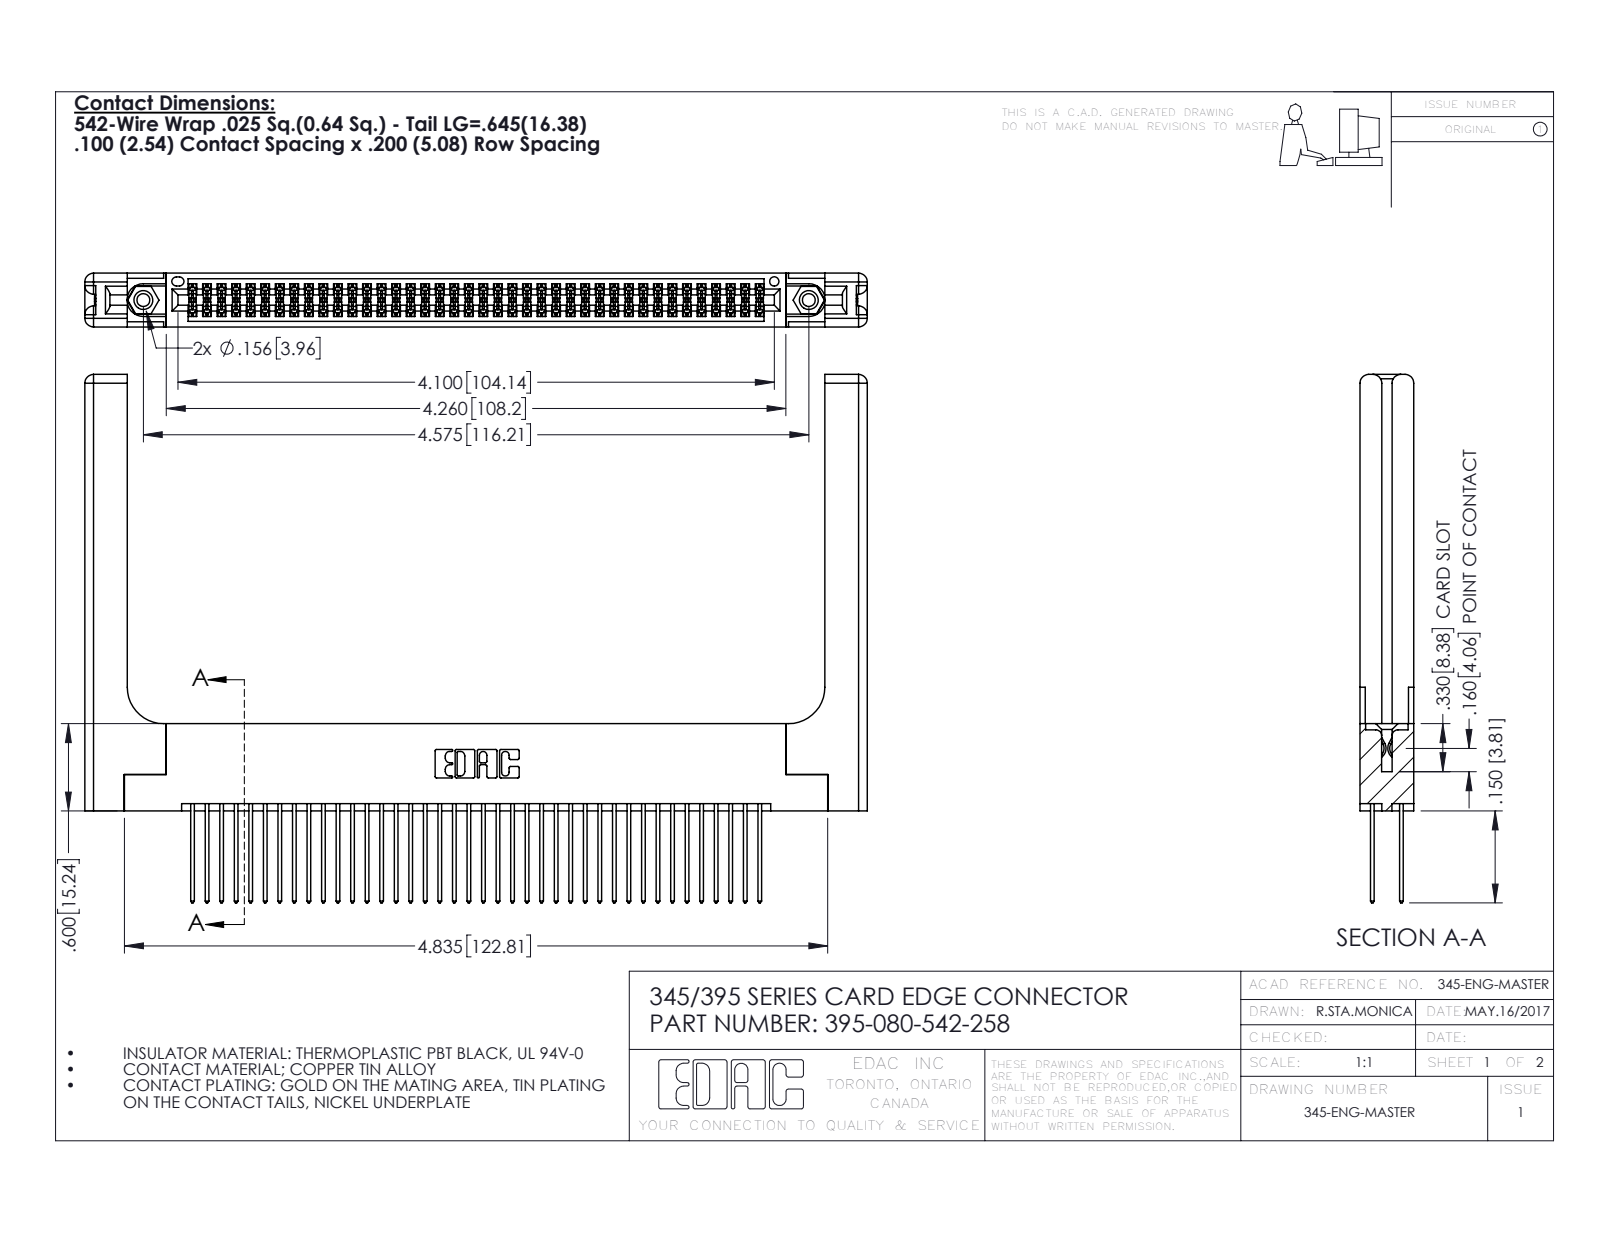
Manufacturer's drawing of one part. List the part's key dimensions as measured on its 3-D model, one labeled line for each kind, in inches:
Part name (STEP PRODUCT): 345-250-001_345-250-001-102; 345 Part_Flush Mounting Lugs - 0.156 Dia-TH; 395-080-542-258; 345-292-001_345-293-142 (+1 more)
STEP written by: SolidWorks 2016 (CONFIG_CONTROL_DESIGN)
Units: inches
Bodies: 85 solids, 4382 faces (2868 planar, 1454 cylindrical, 60 other)
Overall size (bounding box): 5.379 × 3.632 × 0.37
Volume: 1.349 in³ · Surface area: 41.7 in²
Round holes (diameter × count): ⌀0.089 ×2, ⌀0.125 ×2, ⌀0.156 ×2, ⌀0.064 ×1
Round bosses / shafts (diameter × count): ⌀0.155 ×2
Partial cylindrical surfaces — rounded edges, fillets, slot ends (radius × count): R0.006 ×120, R0.01 ×80, R0.01 ×22, R0.06 ×16, R0.007 ×6, R0.031 ×6, R0.026 ×3, R0.014 ×2
Main face-to-face distances: 0.072, 0.298, 0.37, 0.2, 0.098, 0.272, 0.025, 0.225, 0.175, 0.148
Hole centre spacings: 0.27, 4.339, 4.575
